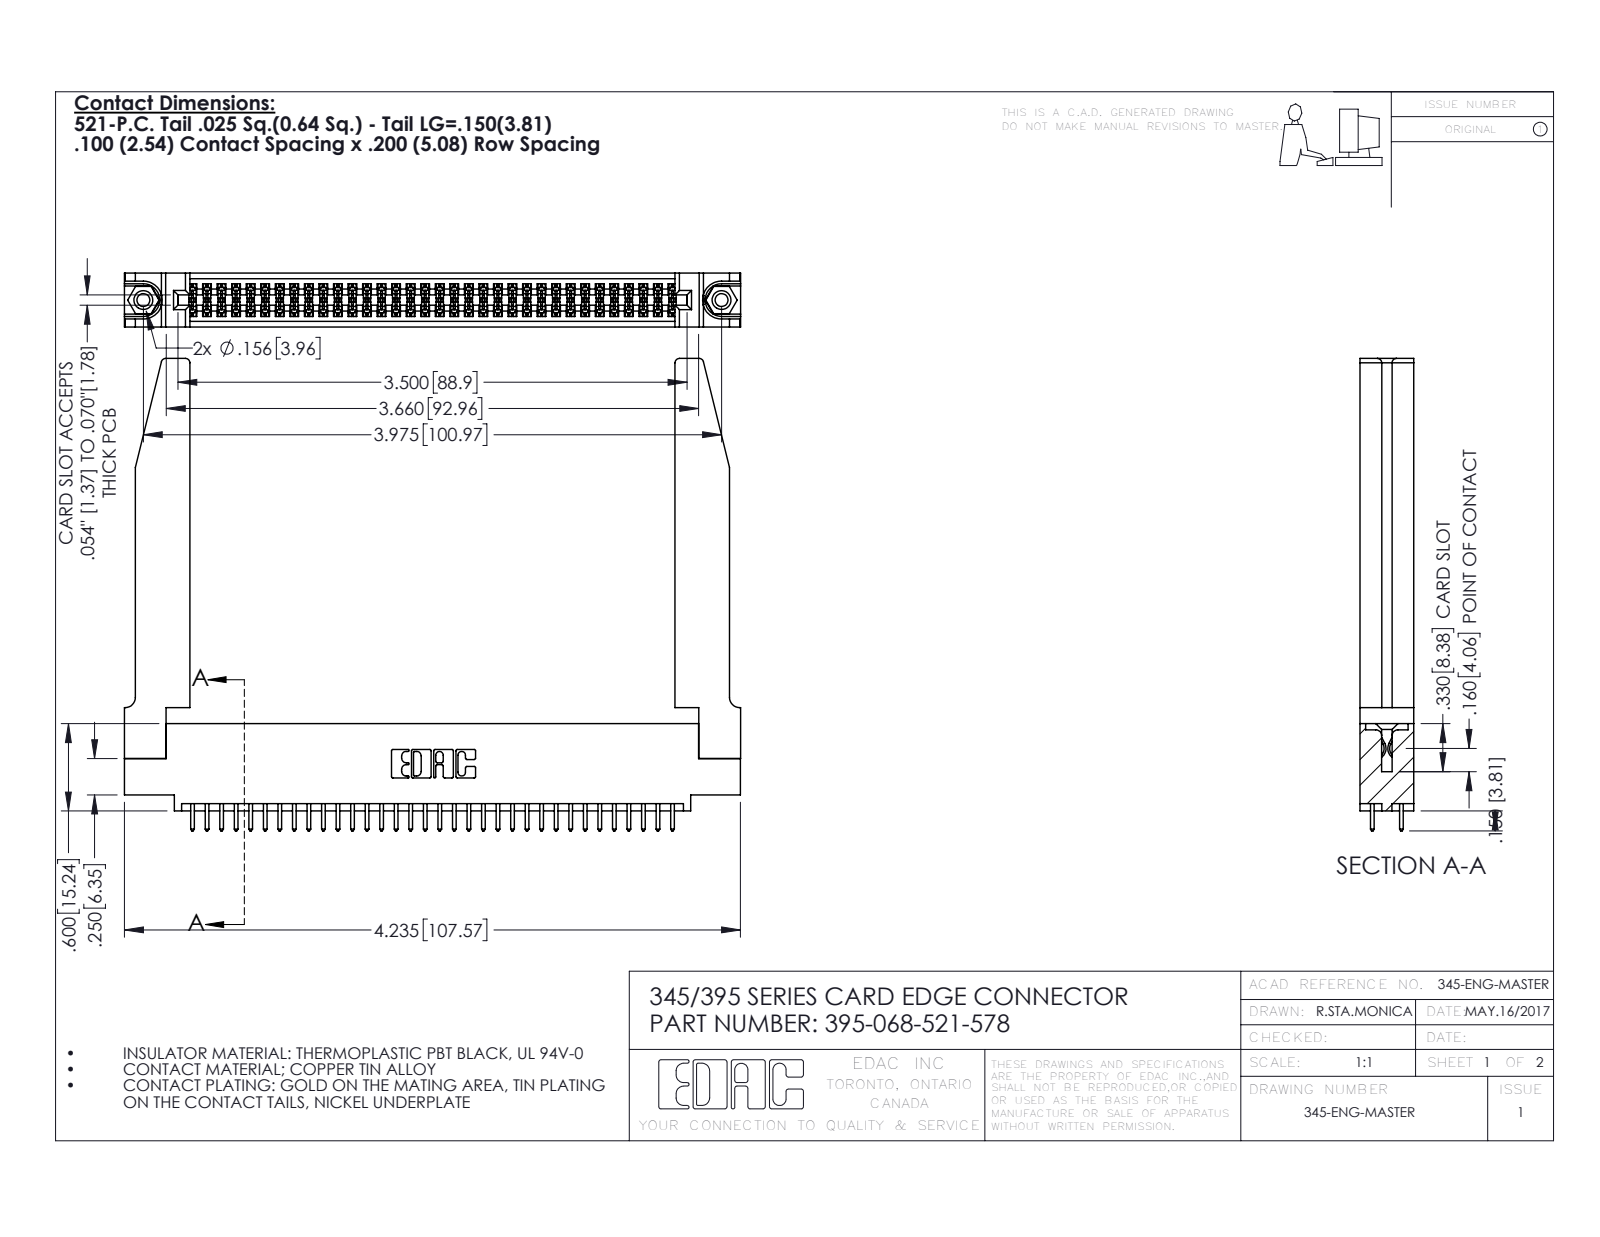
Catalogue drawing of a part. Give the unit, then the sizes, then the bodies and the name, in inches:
Units: inches
Overall size (bounding box): 4.236 × 3.247 × 0.37
Round holes (diameter × count): ⌀0.089 ×2, ⌀0.125 ×2, ⌀0.156 ×2, ⌀0.064 ×1
Round bosses / shafts (diameter × count): ⌀0.155 ×2
Partial cylindrical surfaces — rounded edges, fillets, slot ends (radius × count): R0.006 ×102, R0.01 ×68, R0.01 ×22, R0.03 ×8, R0.007 ×6, R0.031 ×6, R0.026 ×3, R0.014 ×2
Main face-to-face distances: 0.37, 0.072, 0.298, 0.2, 0.098, 0.272, 0.025, 0.225, 0.15, 0.148
Hole centre spacings: 0.27, 3.74, 3.975
Volume: 1.101 in³ · Surface area: 33.77 in²
Bodies: 73 solids, 3764 faces (2470 planar, 1242 cylindrical, 52 other)
Part name (STEP PRODUCT): 345 Part_0.110 Offset - 0.156 Dia-TH; 345-292-001_345-293-121; 395-068-521-578; 345-220-078_345-220-078 (+1 more)
STEP written by: SolidWorks 2016 (CONFIG_CONTROL_DESIGN)
